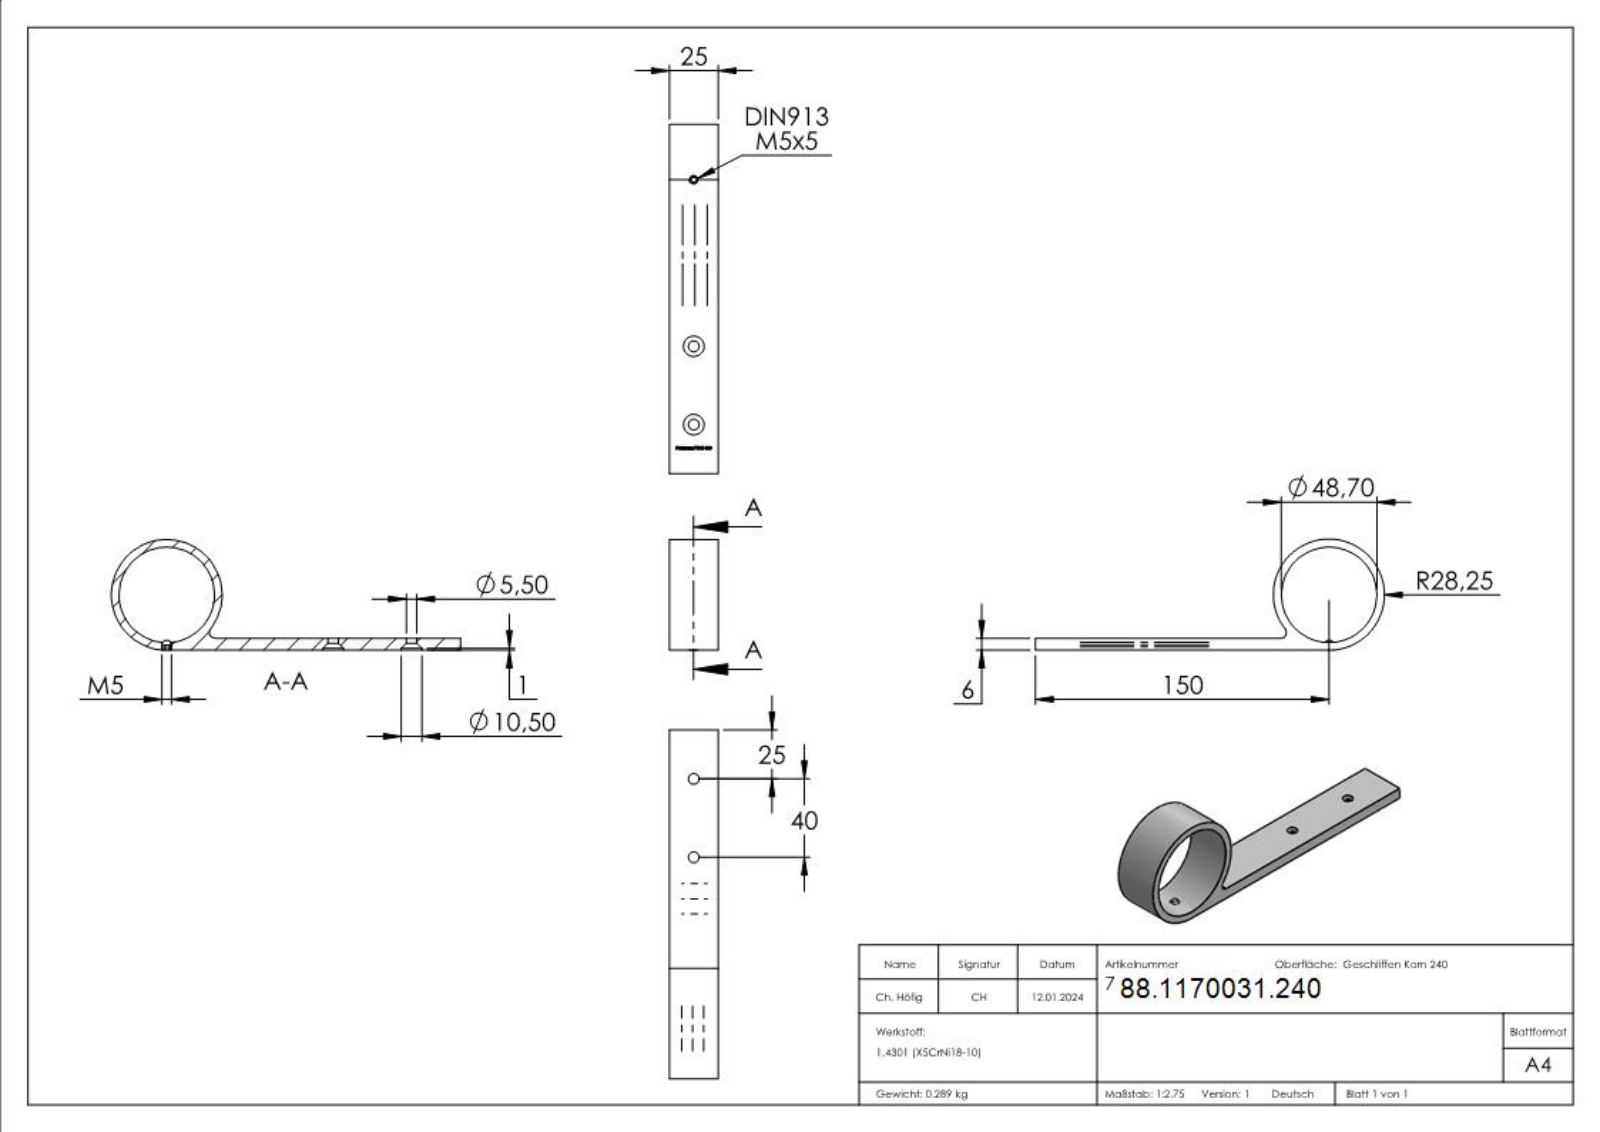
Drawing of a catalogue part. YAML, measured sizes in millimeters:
part_name: "7003X-XXX Teil1_70031-240 Teil1; 70031-240; DIN913 M5x5_DIN913 M5x5"
step_written_by: "SolidWorks 2015 (CONFIG_CONTROL_DESIGN)"
units: millimeters
bodies: {solids: 2, faces: 252, planar: 130, cylindrical: 19, other: 103}
overall_size: [178.25, 56.5, 25]
volume: 36548
surface_area: 18055
round_holes:
  - {diameter: 5.5, count: 2}
  - {diameter: 10.5, count: 2}
  - {diameter: 4.2, count: 1}
  - {diameter: 48.7, count: 1}
round_bosses_or_shafts:
  - {diameter: 56.5, count: 1}
  - {diameter: 5, count: 1}
partial_cylinders:
  - {radius: 3, count: 1}
face_to_face_distances: [6, 25, 2.5, 5.9, 2.4, 3.5, 1, 5, 4.9, 148.75]
hole_center_spacings: [40, 85, 125]
